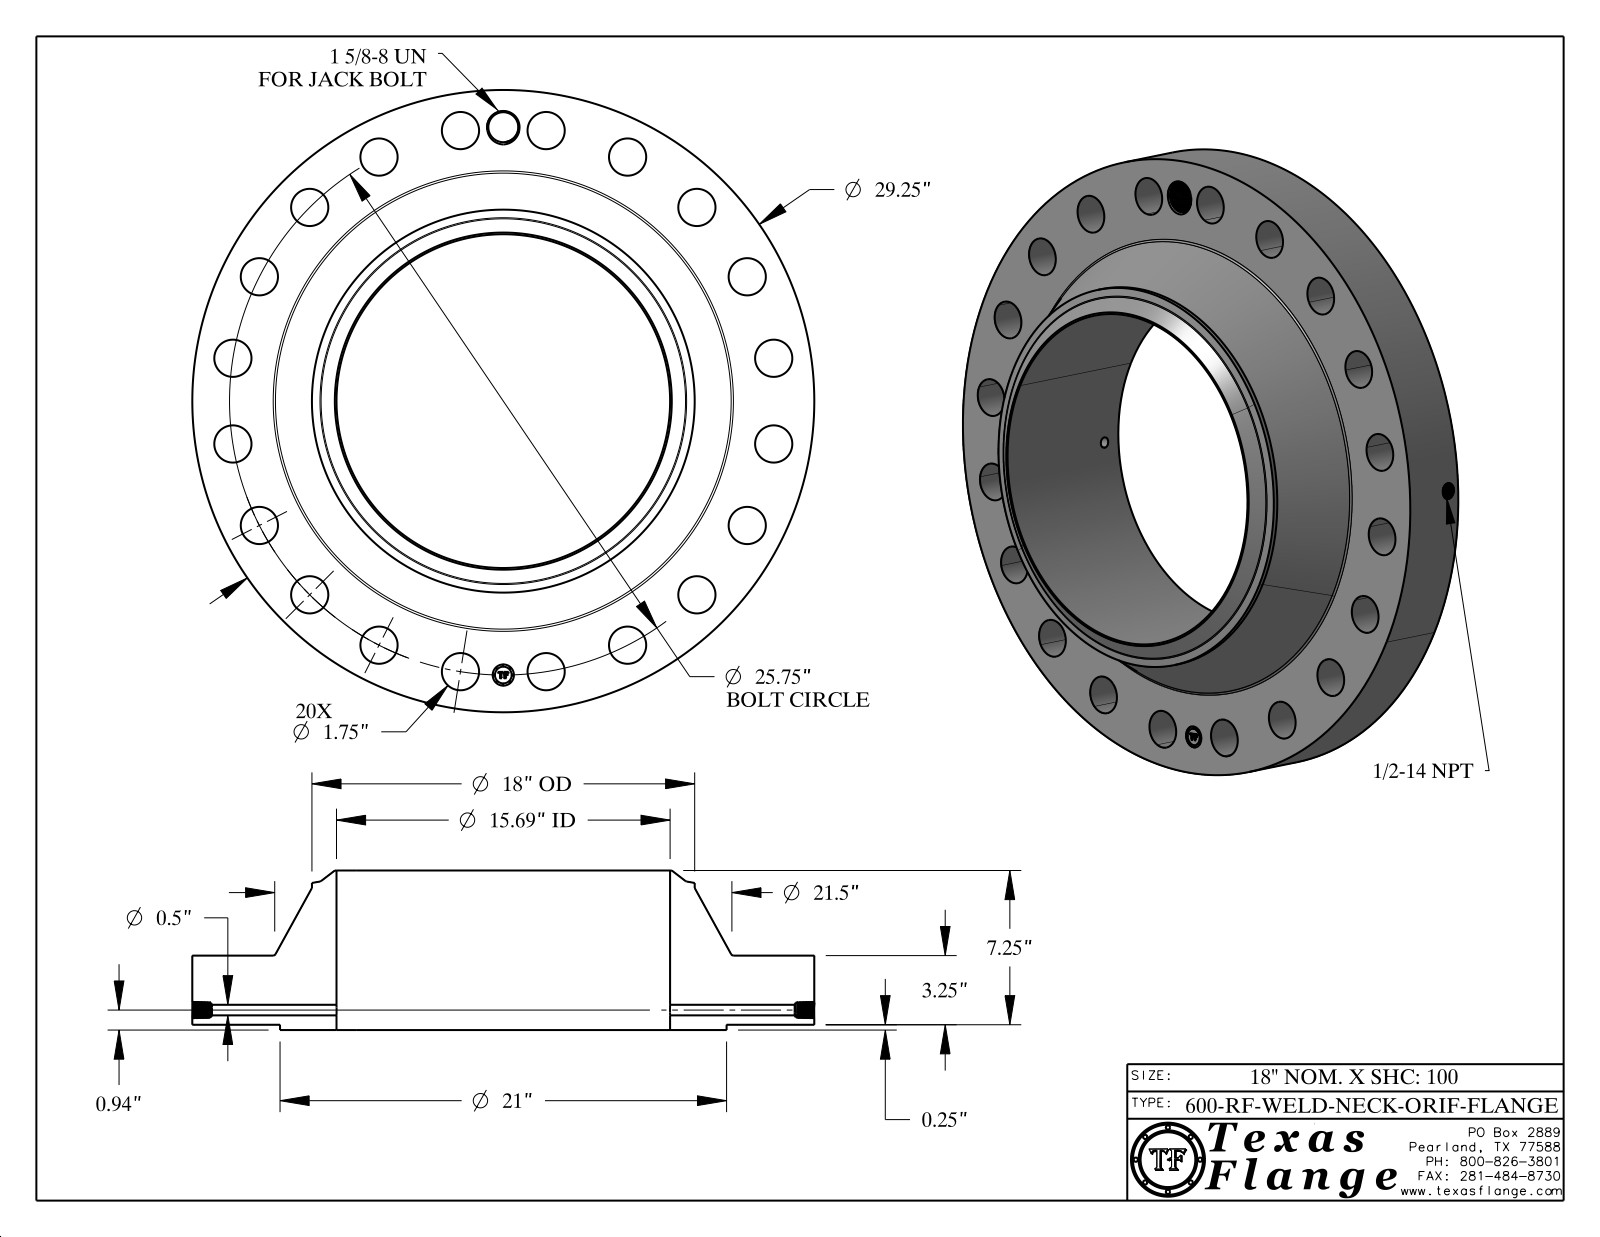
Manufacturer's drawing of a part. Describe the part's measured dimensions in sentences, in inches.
The part is named "600-RF-WELD-NECK". Its 3-D file was written by "CATIA V5 STEP AP214 (AUTOMOTIVE_DESIGN)". It is 1 solid with 863 faces: 369 planar, 139 cylindrical and 355 other. Overall it measures 29.25 by 29.25 by 7.5 inches. Its volume is 1 819 cubic inches and its surface area 2 094 square inches. Round holes: 20 of diameter 1.75, 1 of diameter 0.5, 1 of diameter 0.672, 1 of diameter 1, 1 of diameter 1.409, 1 of diameter 15.688. Round bosses or shafts: 8 of diameter 0.061, 1 of diameter 29.25, 1 of diameter 21, 1 of diameter 18, 1 of diameter 0.788. The main face-to-face distances are 3.25, 0.25, 3.5, 7.5, 7.25, 4, 0.015, 3.485, 3.235, 4.015. The hole center spacings are 15.135, 24.49, 25.433, 12.875, 11.69, 4.028, 7.957, 18.208.
